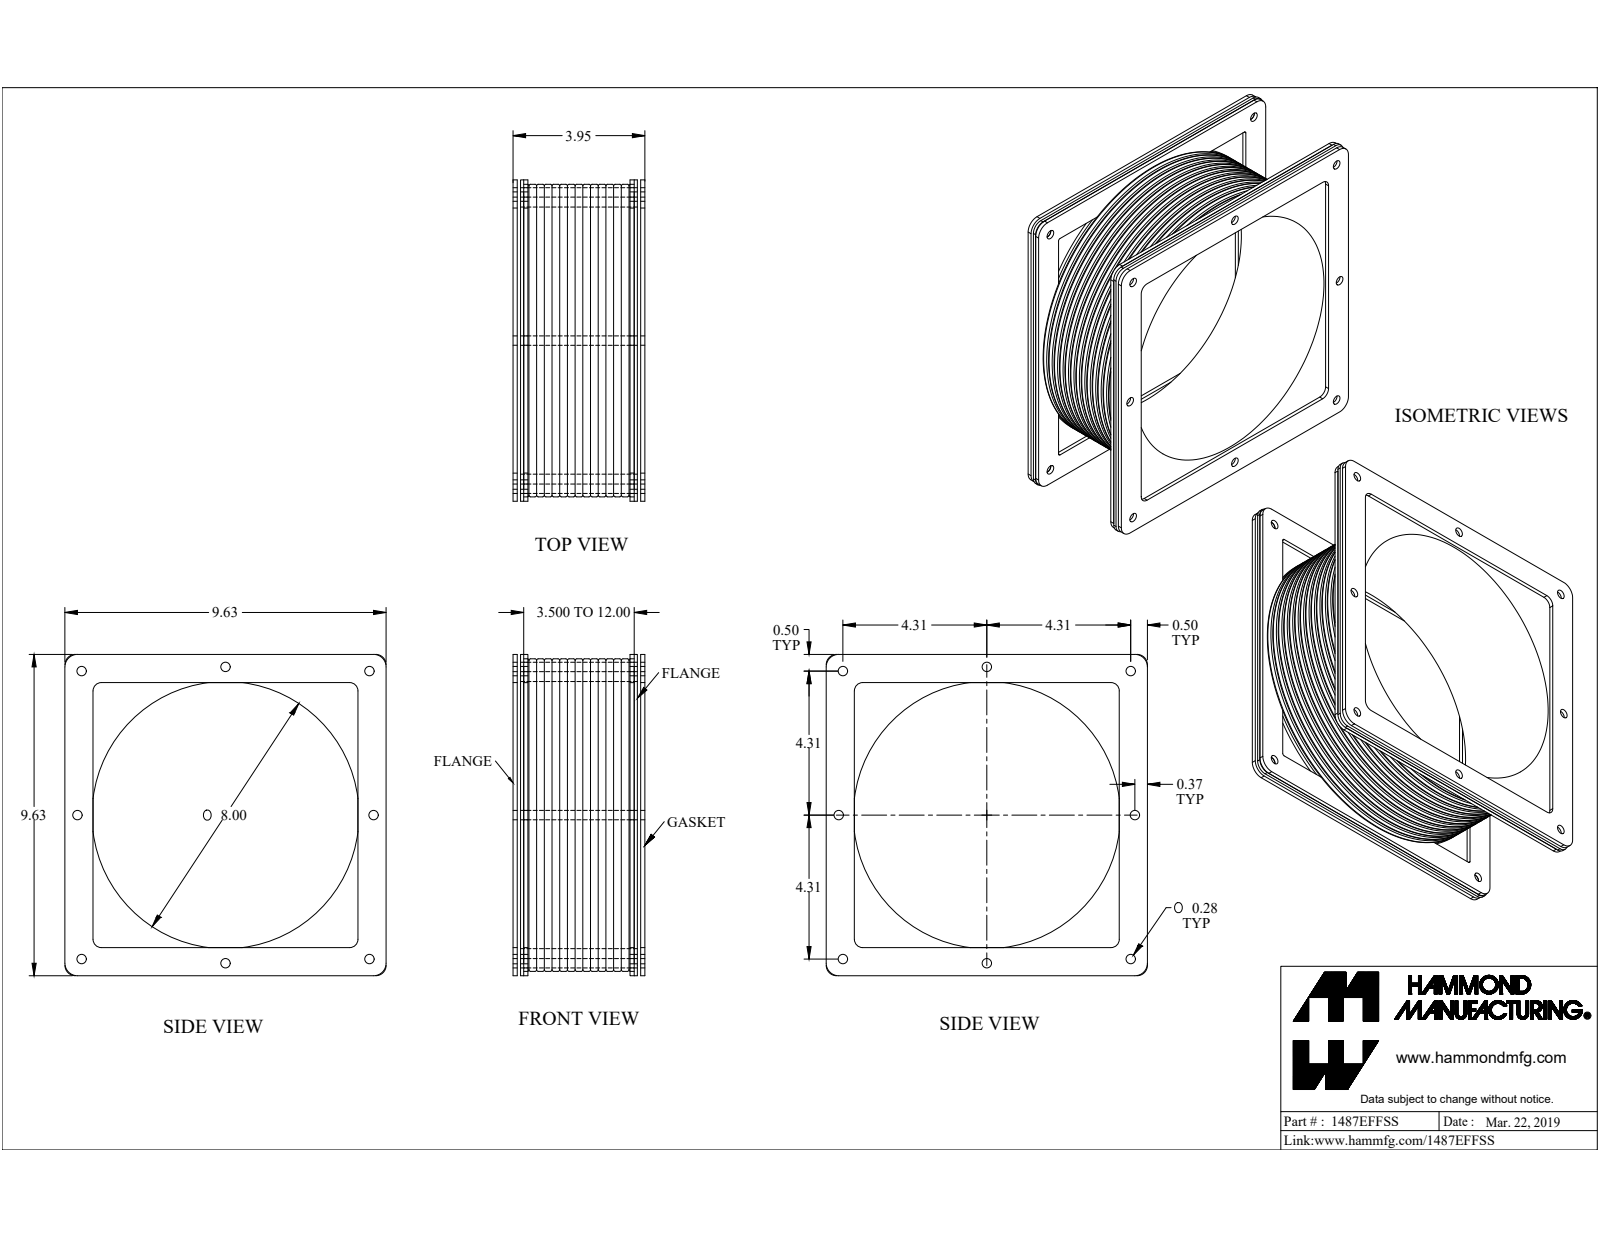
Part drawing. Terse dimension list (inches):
name: 1487EFFSS
written by: SolidWorks 2019 (CONFIG_CONTROL_DESIGN)
unit: in
bodies: 11 solids, 354 faces (166 planar, 144 cylindrical, 44 other)
size: 9.625 × 9.625 × 4.501
volume: 82.79 in³; area: 634.4 in²
holes: 8× ⌀0.281, 8× ⌀0.281, 1× ⌀0.196, 1× ⌀0.258, 1× ⌀0.35, 1× ⌀8
bosses: 1× ⌀9.362, 1× ⌀0.5, 1× ⌀0.25
rounds: 12× R0.02, 4× R0.063, 4× R0.25, 4× R0.313, 4× R0.375
face distances: 0.095, 3.405, 0.22, 3.28, 0.125, 3.185, 0.1, 0.195, 0.32, 3.38
hole spacings: 4.315, 9.755, 4.437, 6.099, 6.276, 8.625, 8.875, 12.198
